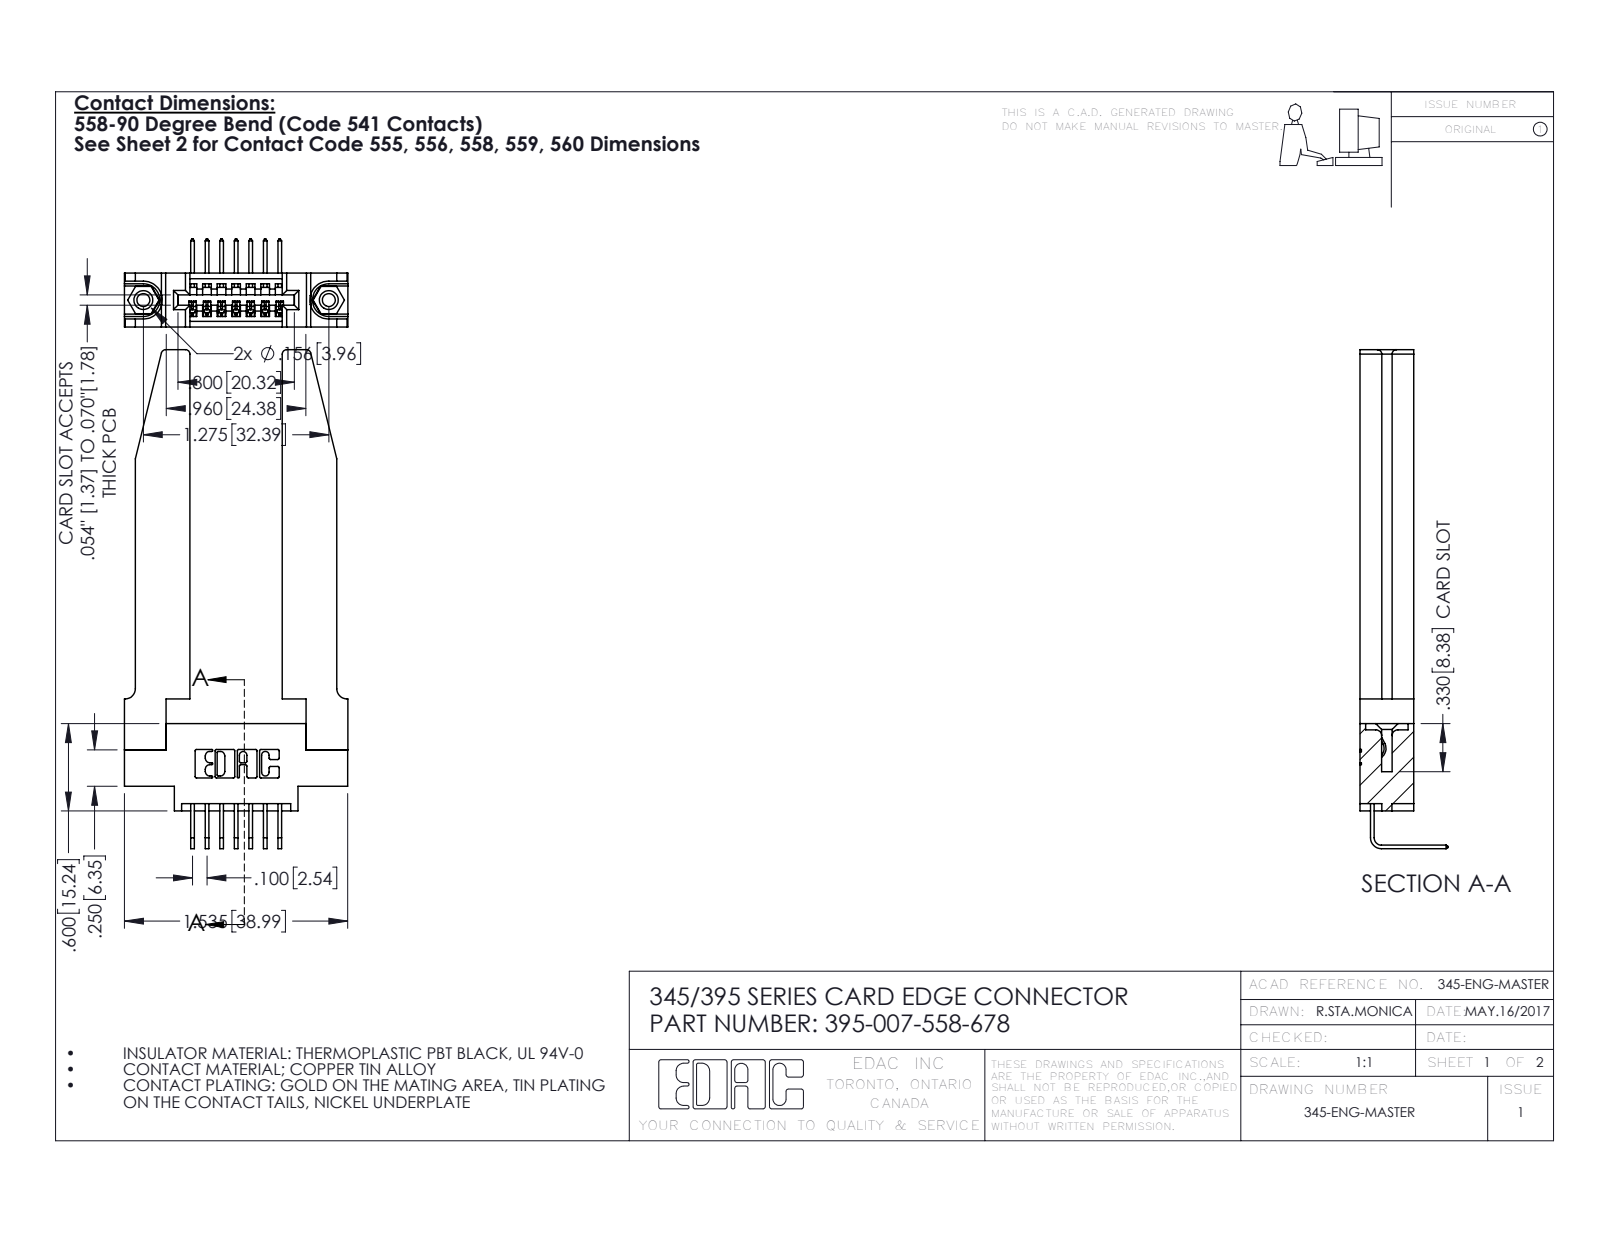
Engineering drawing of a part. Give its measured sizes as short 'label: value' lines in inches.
name: 345-250-001_345-250-001-102; 345 Part_0.170 Offset - 0.156 Dia-TH; 345-220-078_345-220-078; 345-292-001_558 Tail - 2 (+1 more)
written by: SolidWorks 2016 (CONFIG_CONTROL_DESIGN)
unit: in
bodies: 12 solids, 784 faces (520 planar, 212 cylindrical, 52 other)
size: 3.429 × 1.536 × 0.605
volume: 0.677 in³; area: 17.14 in²
holes: 2× ⌀0.089, 2× ⌀0.125, 2× ⌀0.156, 1× ⌀0.064
bosses: 2× ⌀0.155
rounds: 22× R0.01, 14× R0.006, 8× R0.03, 6× R0.007, 6× R0.031, 3× R0.026, 2× R0.031, 2× R0.04
face distances: 0.37, 0.15, 0.22, 0.072, 0.148, 0.635, 0.298, 0.077, 0.095, 0.071
hole spacings: 0.27, 1.045, 1.275
